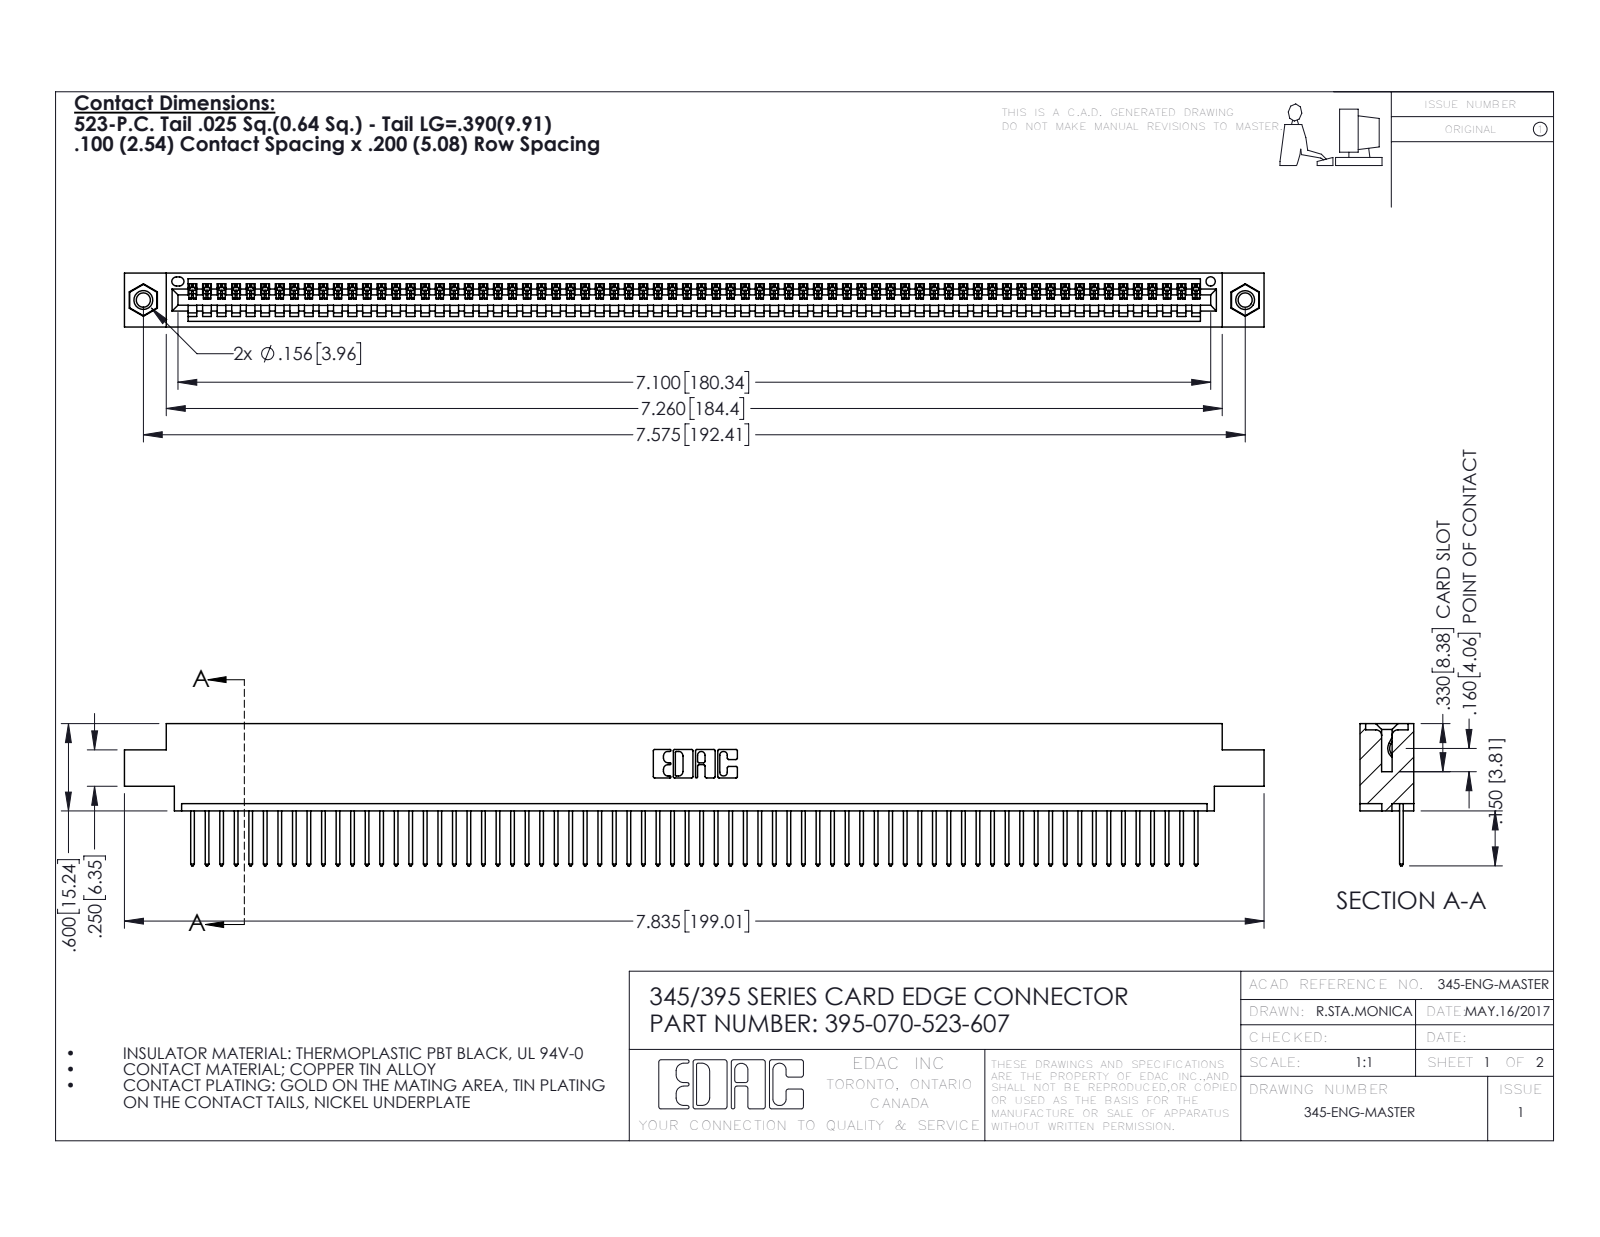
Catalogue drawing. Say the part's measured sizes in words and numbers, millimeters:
The part is named "345-250-001_345-250-005-103; 395-070-523-607; 345 Part_0.170 Offset - 0.156 Dia-TI; 345-292-001_345-293-123". Its 3-D file was written by "SolidWorks 2016 (CONFIG_CONTROL_DESIGN)". It is 73 solids with 4250 faces: 2916 planar, 1318 cylindrical and 16 other. Overall it measures 199 by 24.8 by 9.4 millimeters. Its volume is 18 980 cubic millimeters and its surface area 25 830 square millimeters. Round holes: 2 of diameter 2.5, 2 of diameter 3.2, 2 of diameter 4, 1 of diameter 1.6. Round bosses or shafts: 2 of diameter 3.9. Partial cylindrical surfaces (rounded edges, fillets, slot ends): 140 of radius 0.2, 140 of radius 0.3, 22 of radius 0.3, 6 of radius 0.2, 6 of radius 0.8, 3 of radius 0.7, 2 of radius 0.8, 2 of radius 1. The main face-to-face distances are 1.8, 7.6, 9.4, 2.5, 6.9, 0.6, 5.1, 5.7, 4.4, 3.8. The hole center spacings are 6.9, 186.4, 192.4.
